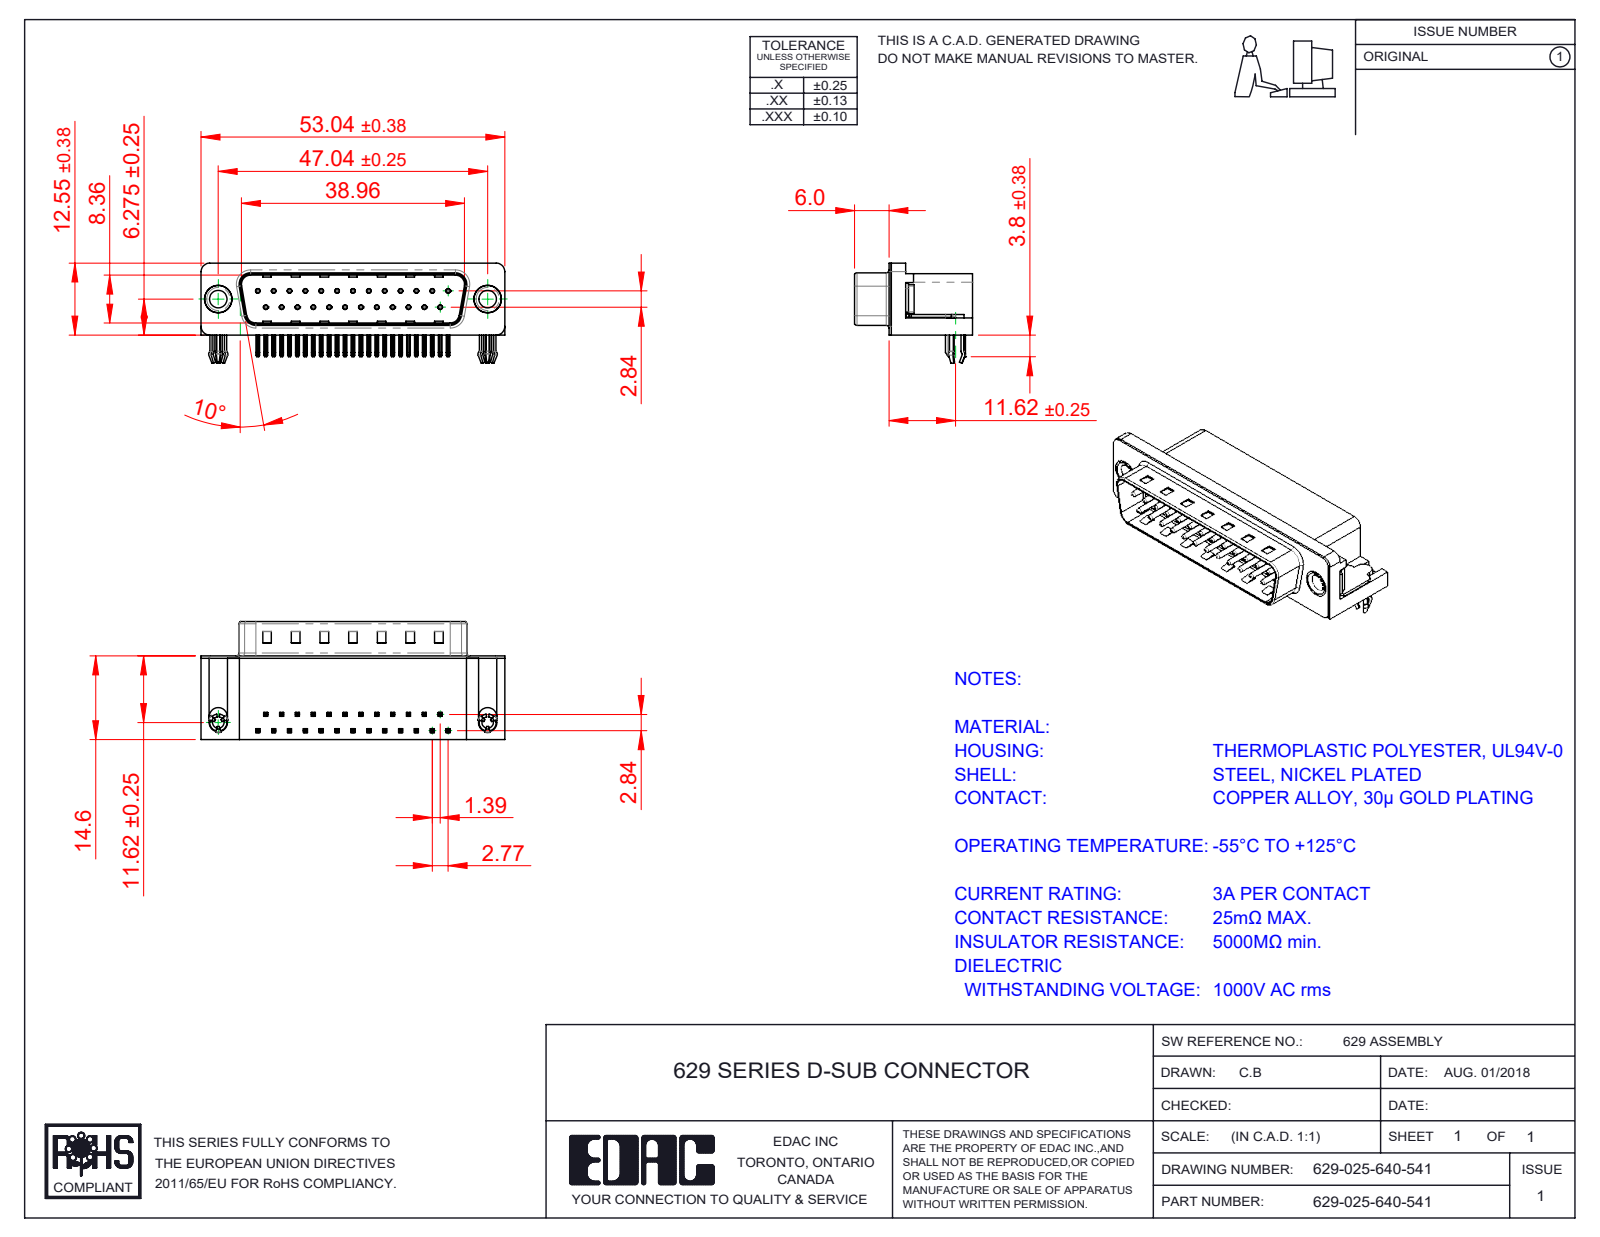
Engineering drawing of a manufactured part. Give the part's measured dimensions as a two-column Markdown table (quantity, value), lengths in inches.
| quantity | value |
| --- | --- |
| part name | 629 Contact Top; 629 3 Prong Board Lock; 629-025-640-541; 629 Shell_25 Socket (+3 more) |
| STEP written by | SolidWorks 2020 (CONFIG_CONTROL_DESIGN) |
| units | inches |
| bodies | 31 solids, 2325 faces (1441 planar, 647 cylindrical, 237 other) |
| overall size | 2.088 × 0.811 × 0.688 |
| volume | 0.447 in³ |
| surface area | 12.84 in² |
| round holes (diameter × count) | 0.014 × 25, 0.031 × 25, 0.079 × 2, 0.12 × 2, 0.157 × 2, 0.189 × 2, 0.197 × 2 |
| round bosses / shafts (diameter × count) | 0.03 × 25, 0.193 × 2, 0.187 × 2, 0.152 × 2, 0.118 × 2 |
| partial cylindrical surfaces (radius × count) | 0.01 × 112, 0.005 × 50, 0.039 × 16, 0.02 × 9, 0.063 × 8, 0.059 × 7, 0.035 × 4, 0.079 × 4 |
| main face-to-face distances | 0.016, 0.408, 0.559, 0.083, 0.345, 0.067, 0.412, 0.428, 0.575, 0.114 |
| hole center spacings | 0.124, 0.109, 0.218, 0.327, 0.436, 0.545, 0.654, 0.198 |
